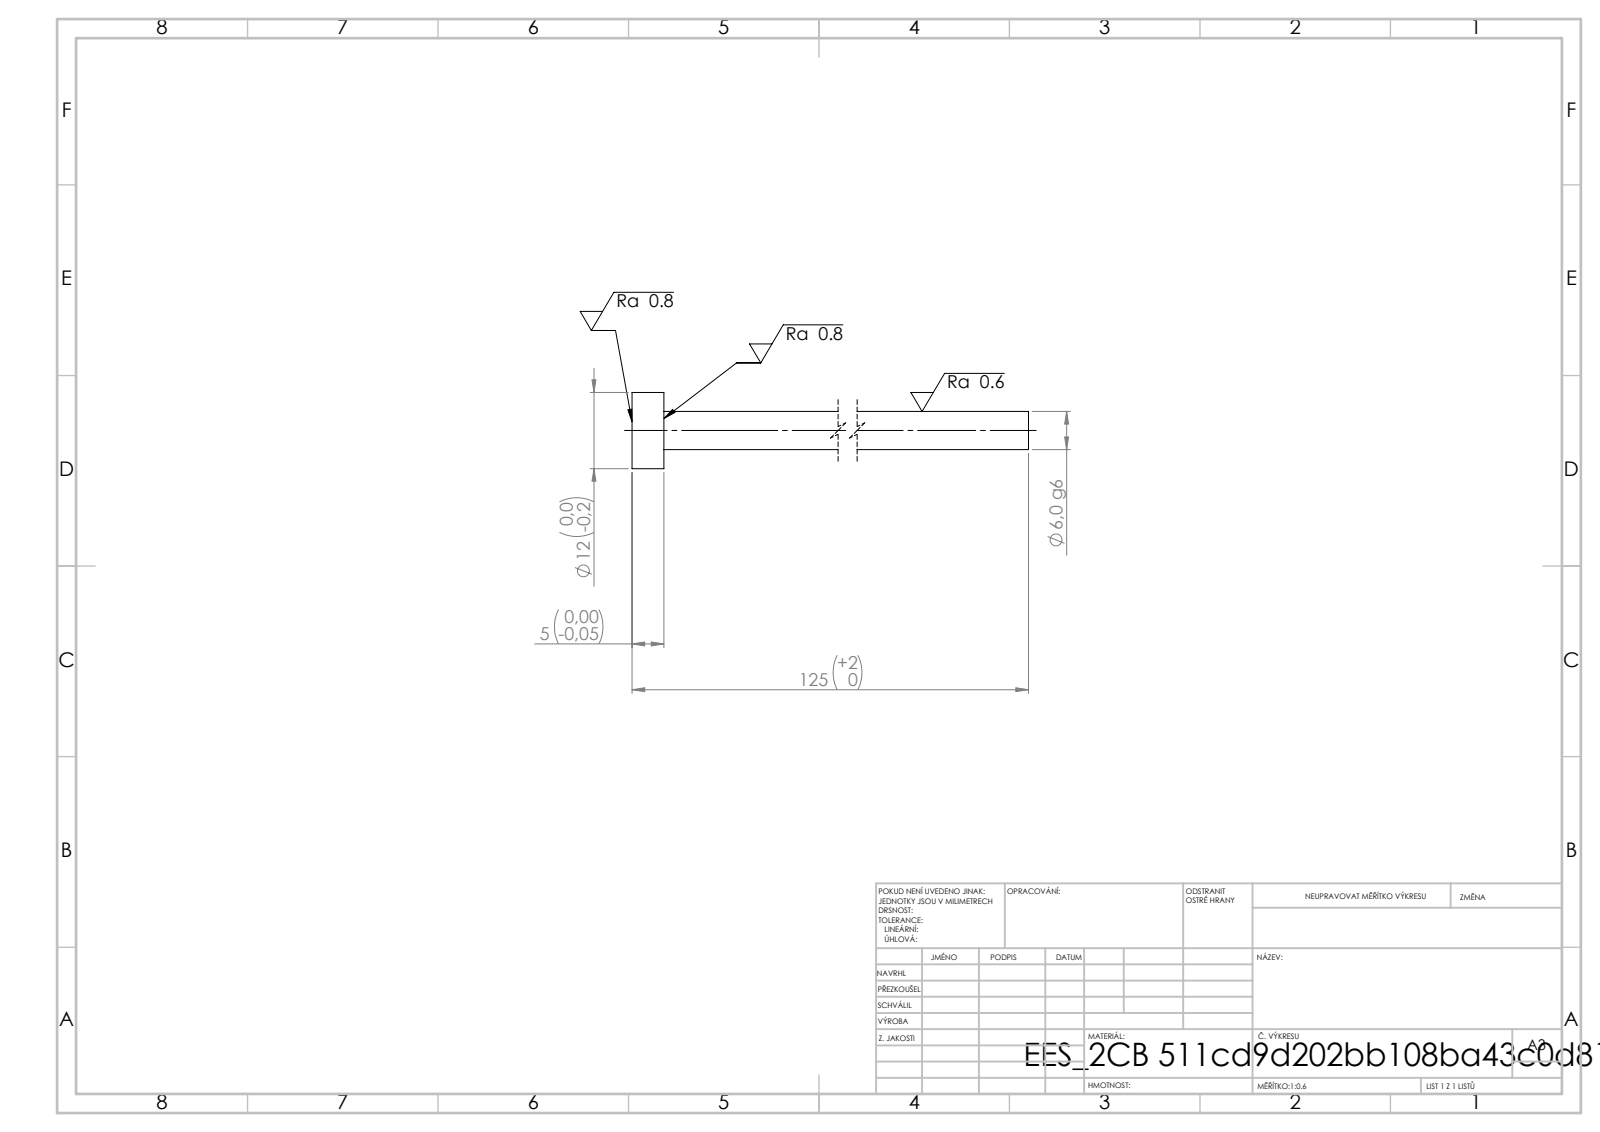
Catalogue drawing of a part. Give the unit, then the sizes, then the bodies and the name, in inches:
Units: inches
Overall size (bounding box): 4.921 × 0.472 × 0.472
Round bosses / shafts (diameter × count): ⌀0.472 ×1, ⌀0.236 ×1
Main face-to-face distances: 0.197, 4.921, 4.724
Volume: 0.242 in³ · Surface area: 4.149 in²
Bodies: 1 solid, 7 faces (3 planar, 4 cylindrical, 0 other)
STEP written by: SolidWorks 2019 (CONFIG_CONTROL_DESIGN)
